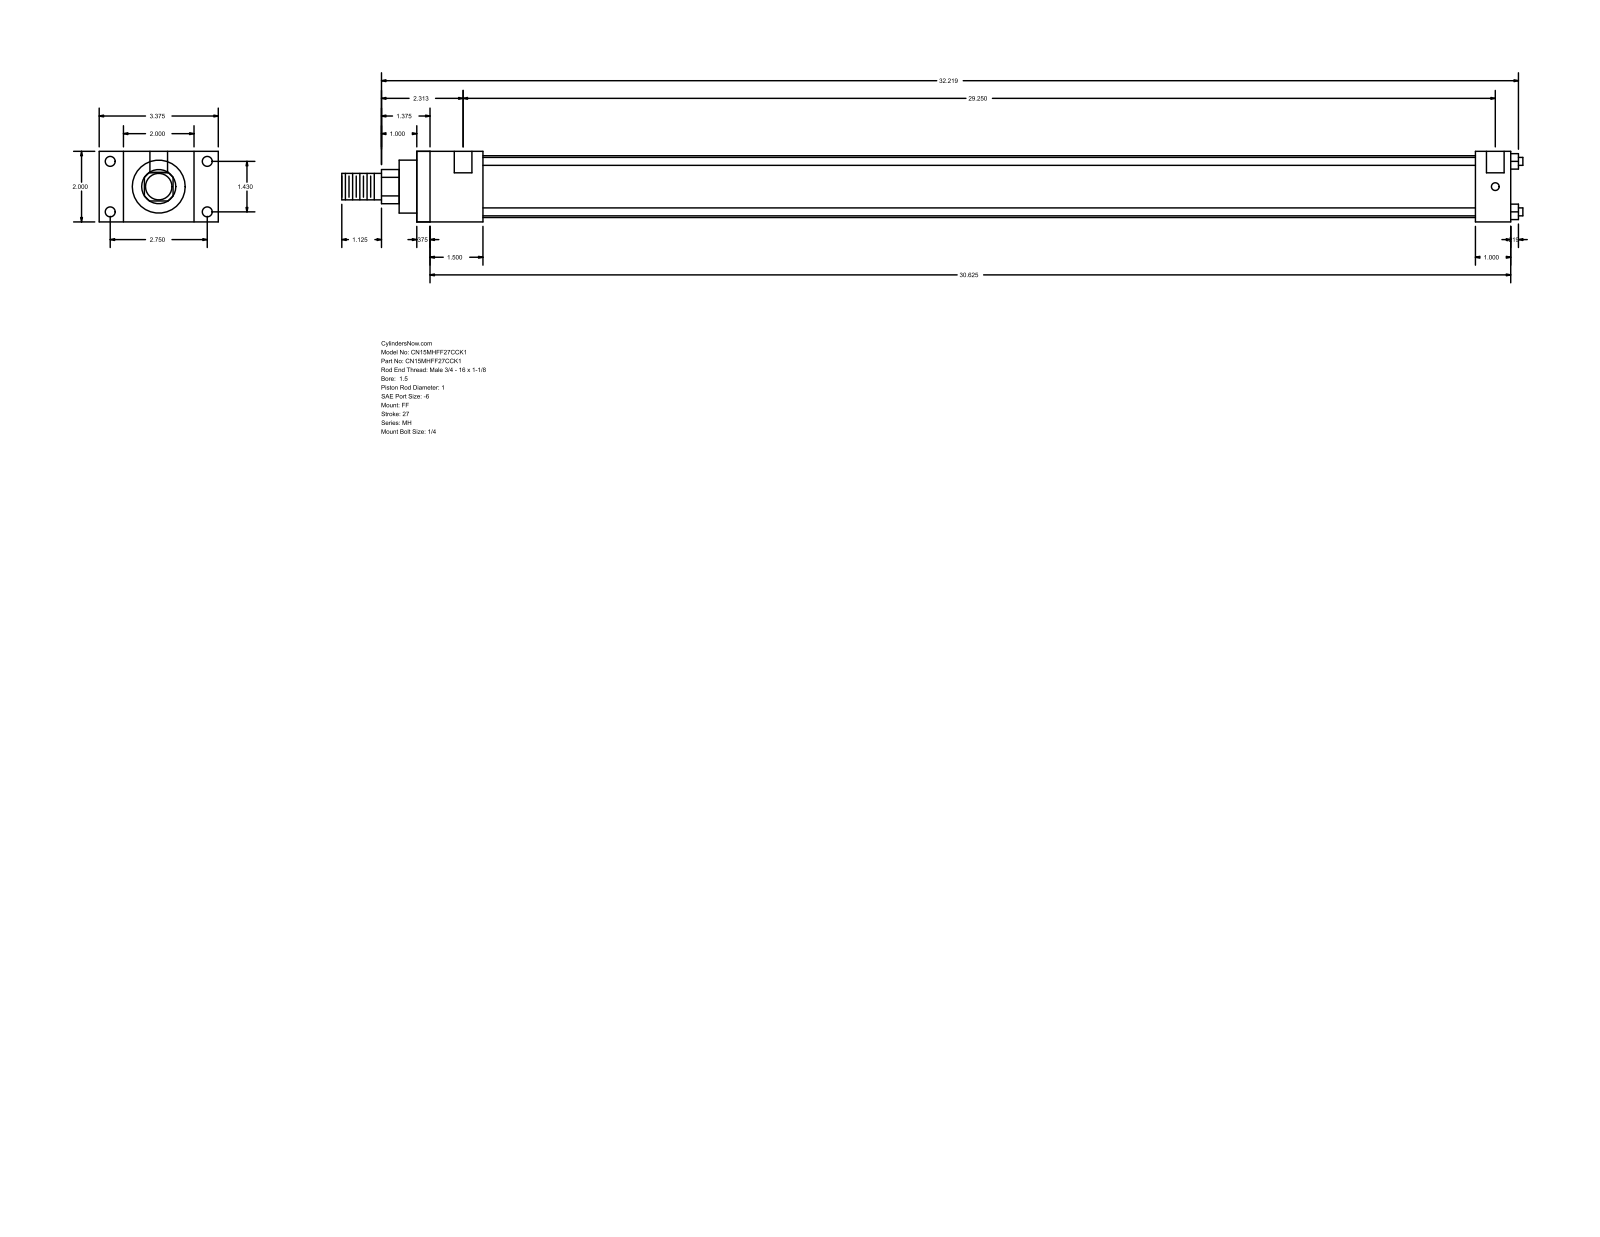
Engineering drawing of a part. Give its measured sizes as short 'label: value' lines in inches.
name: MH_FF__0150_1
written by: GSSL Pune (CONFIG_CONTROL_DESIGN)
unit: in
bodies: 0 solids, 92 faces (64 planar, 28 cylindrical, 0 other)
size: 33.469 × 3.375 × 2
holes: 4× ⌀0.219, 4× ⌀0.281, 2× ⌀0.5
bosses: 4× ⌀0.225, 1× ⌀1.75, 1× ⌀1.5, 1× ⌀1, 1× ⌀0.75
rounds: 1× R0.484
face distances: 2, 31, 0.375, 30.625, 1, 0.687, 2.687, 1.875, 1.5, 29.125
hole spacings: 1.43, 2.75, 3.099, 29.375, 0.125, 29.25
